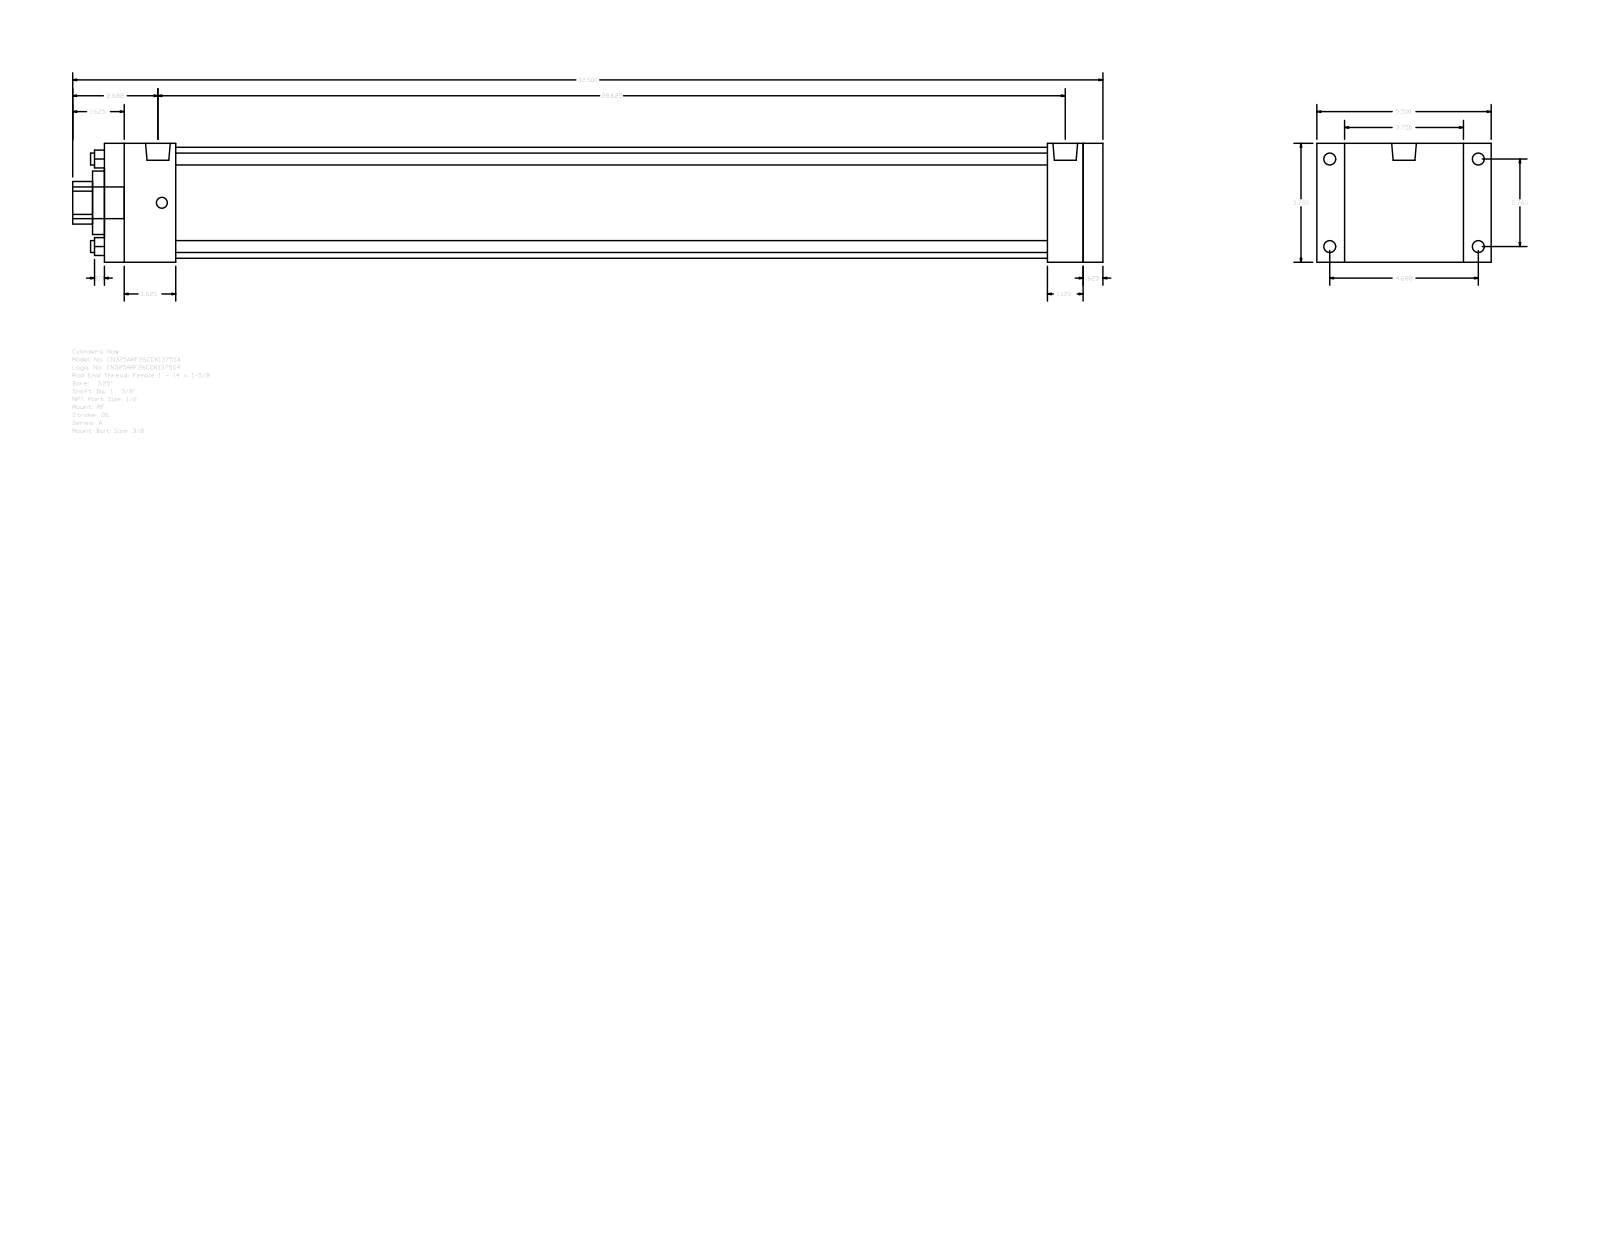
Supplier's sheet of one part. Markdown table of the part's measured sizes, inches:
| quantity | value |
| --- | --- |
| part name | A_RF__0325_1.375 |
| STEP written by | GSSL Pune (CONFIG_CONTROL_DESIGN) |
| units | inches |
| bodies | 0 solids, 92 faces (64 planar, 28 cylindrical, 0 other) |
| overall size | 32.5 × 5.5 × 3.75 |
| round holes (diameter × count) | 0.375 × 4, 1.375 × 1, 2 × 1, 3.5 × 1 |
| round bosses / shafts (diameter × count) | 0.375 × 4, 0.344 × 4, 0.778 × 2, 1 × 1 |
| partial cylindrical surfaces (radius × count) | 0.672 × 1 |
| main face-to-face distances | 3.75, 31.5, 0.625, 30.875, 0.875, 4.625, 1.125, 29.75, 1.75, 2.25 |
| hole center spacings | 1.952, 2.76, 3.903 |
